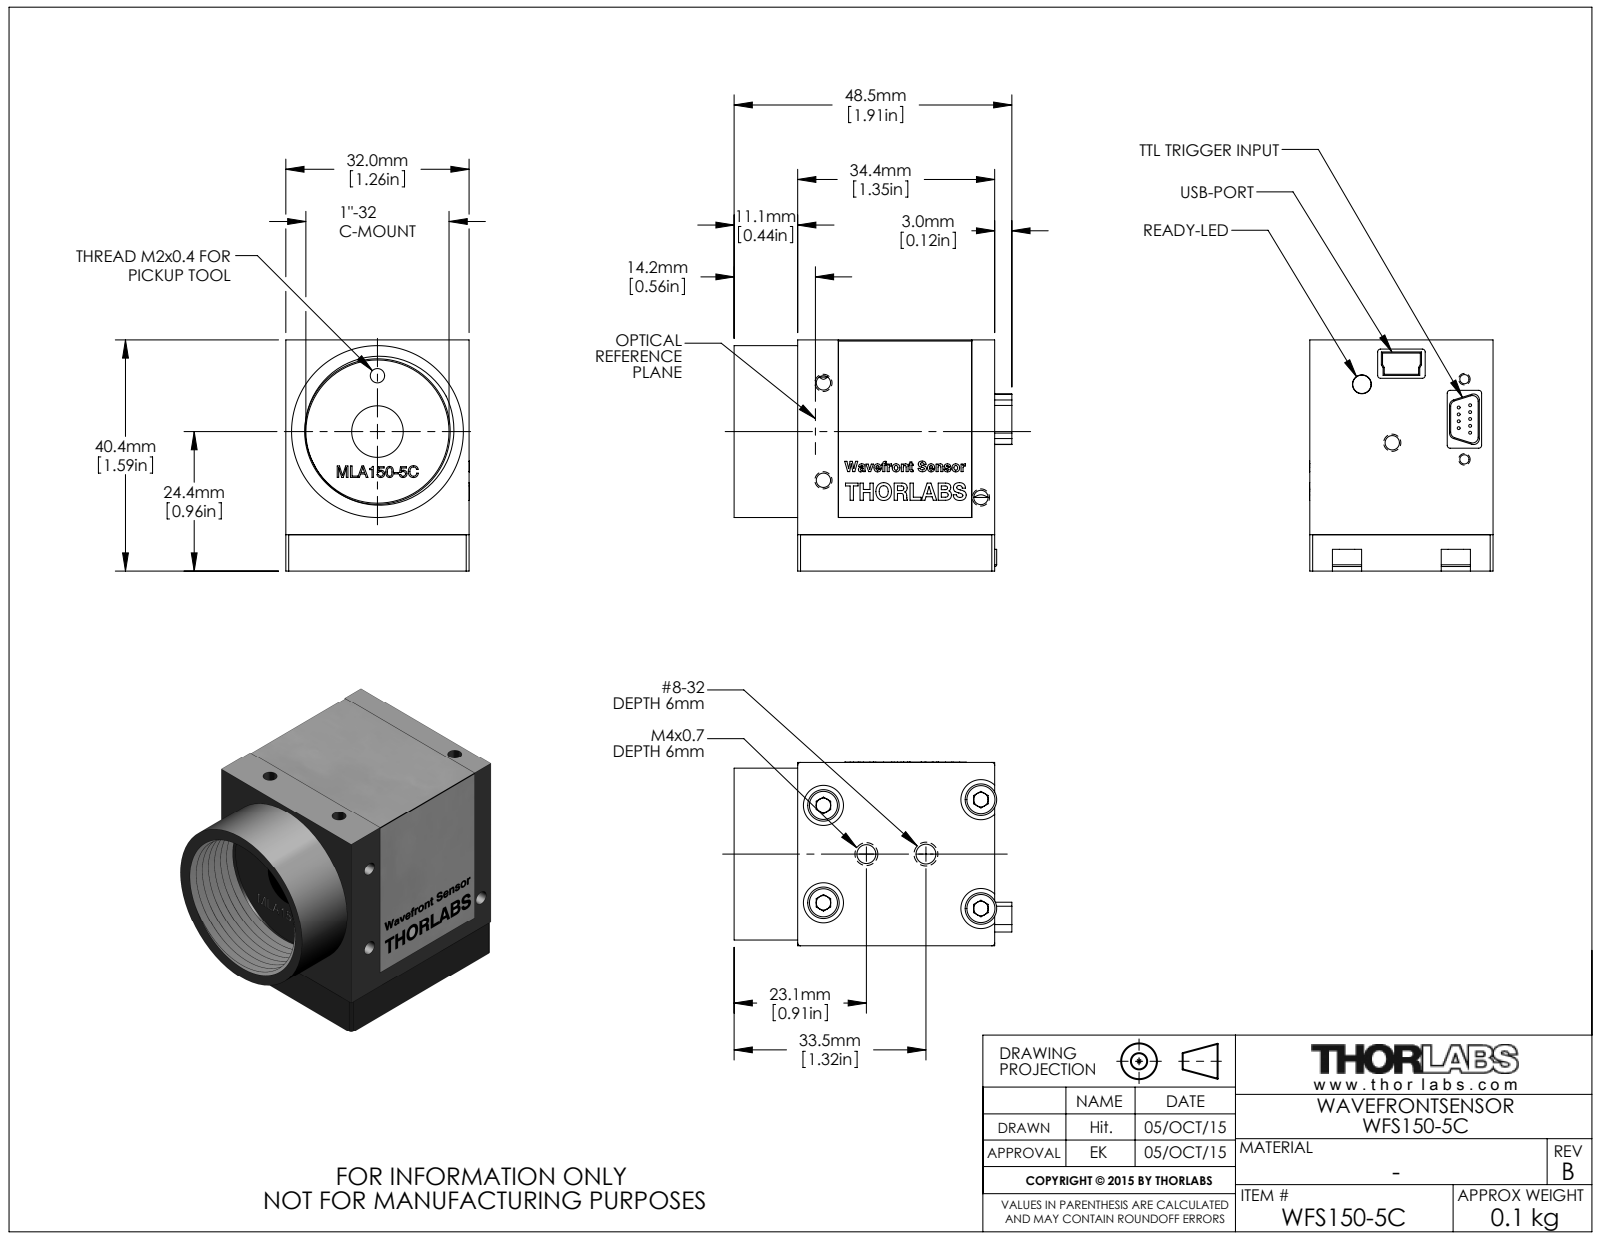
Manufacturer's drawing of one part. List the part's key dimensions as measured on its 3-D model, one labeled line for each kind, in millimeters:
Part name (STEP PRODUCT): 19906-E0W - Rev B
STEP written by: SolidWorks 2014 (AUTOMOTIVE_DESIGN)
Units: millimetres
Bodies: 3 solids, 1015 faces (529 planar, 125 cylindrical, 361 other)
Overall size (bounding box): 48.5 × 40.35 × 32.05
Volume: 44 777 mm³ · Surface area: 14 141 mm²
Round holes (diameter × count): ⌀2.5 ×9, ⌀1.6 ×8, ⌀3.2 ×4, ⌀3.3 ×2, ⌀7 ×2, ⌀3.45 ×1, ⌀9 ×1, ⌀25 ×1
Round bosses / shafts (diameter × count): ⌀0.5 ×9, ⌀30 ×1, ⌀3.2 ×1
Partial cylindrical surfaces — rounded edges, fillets, slot ends (radius × count): R0.5 ×12, R1 ×8, R3.5 ×2
Main face-to-face distances: 34, 34.4, 6.35, 40.35, 31.8, 32, 45.5, 11.1, 3.8, 2.55
Hole centre spacings: 12, 3.2, 3.54, 6.36, 7, 8.28, 10.9, 11.24
